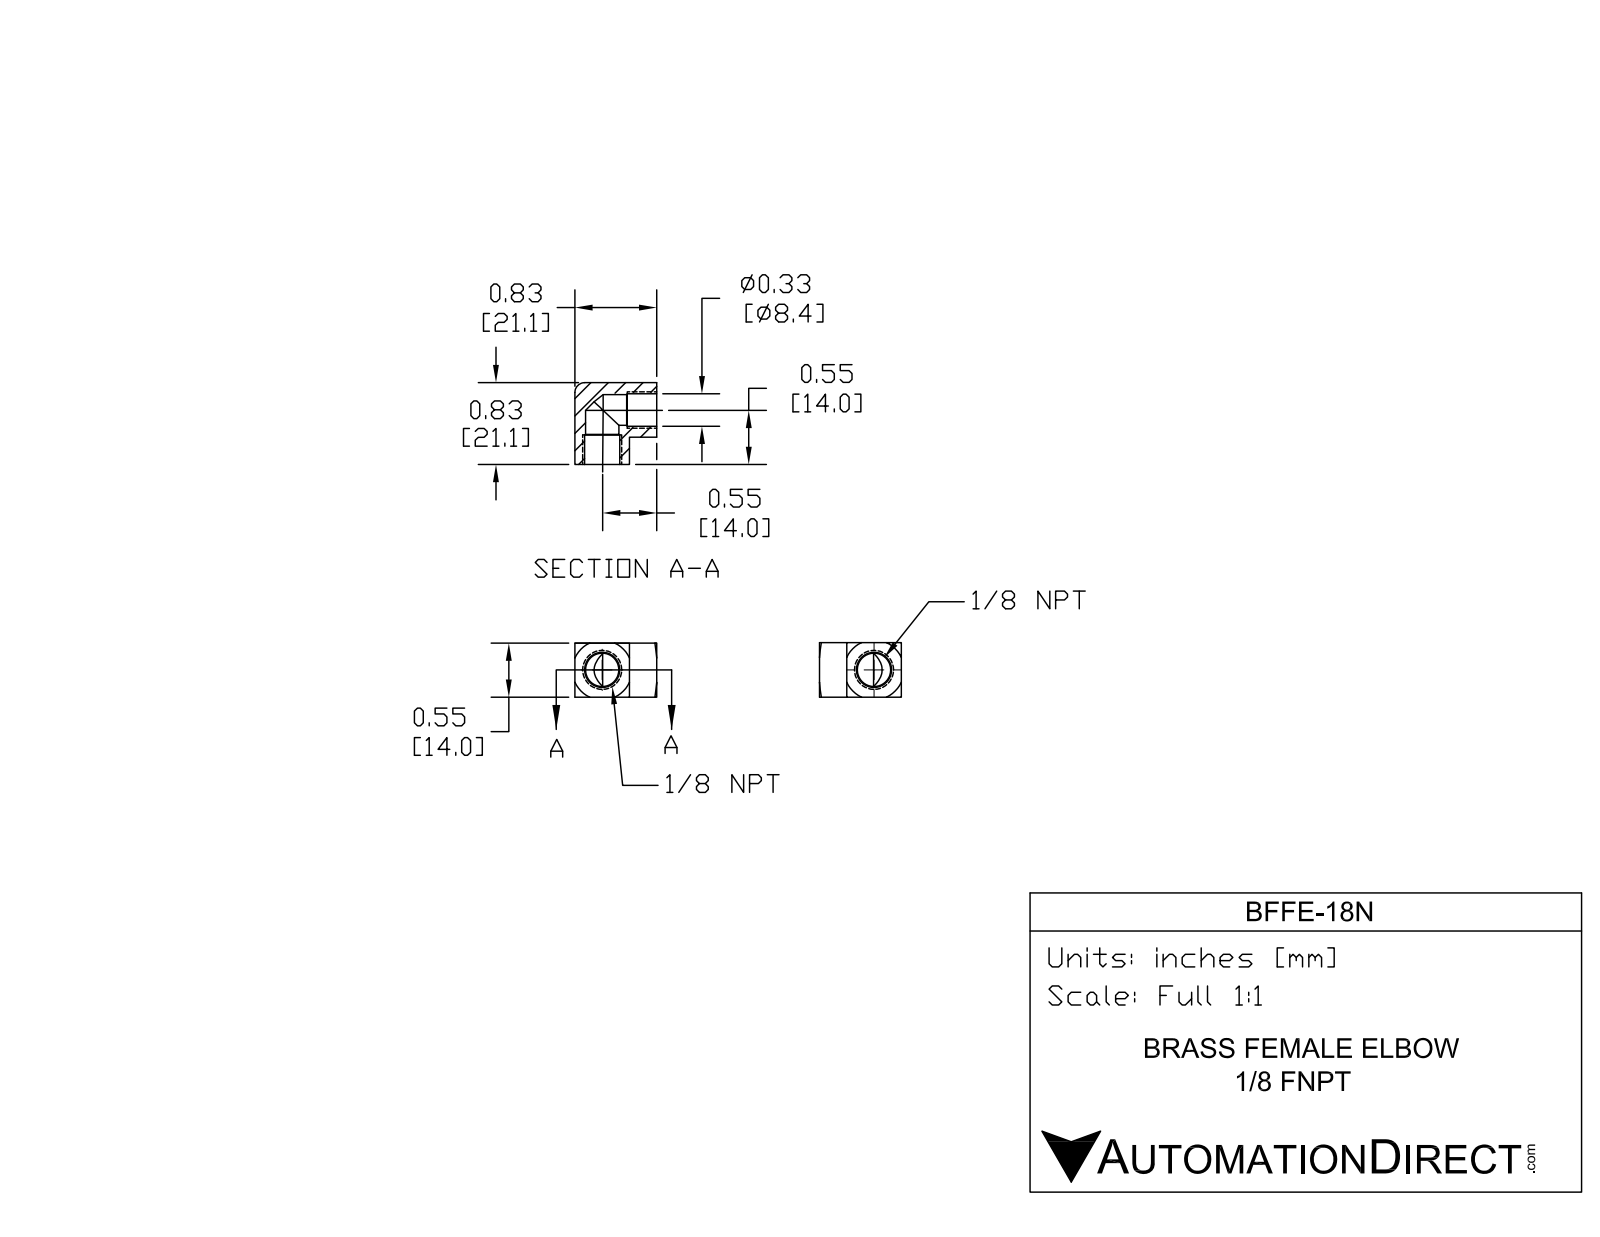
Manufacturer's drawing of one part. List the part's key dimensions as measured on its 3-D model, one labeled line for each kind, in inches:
Part name (STEP PRODUCT): BFFE-18N
STEP written by: SolidWorks 2015 (CONFIG_CONTROL_DESIGN)
Units: inches
Bodies: 1 solid, 32 faces (8 planar, 9 cylindrical, 15 other)
Overall size (bounding box): 0.832 × 0.832 × 0.555
Volume: 0.237 in³ · Surface area: 4.015 in²
Round holes (diameter × count): ⌀0.339 ×2, ⌀0.358 ×2
Partial cylindrical surfaces — rounded edges, fillets, slot ends (radius × count): R0.1 ×1
Main face-to-face distances: 0.555, 0.832, 0.277
